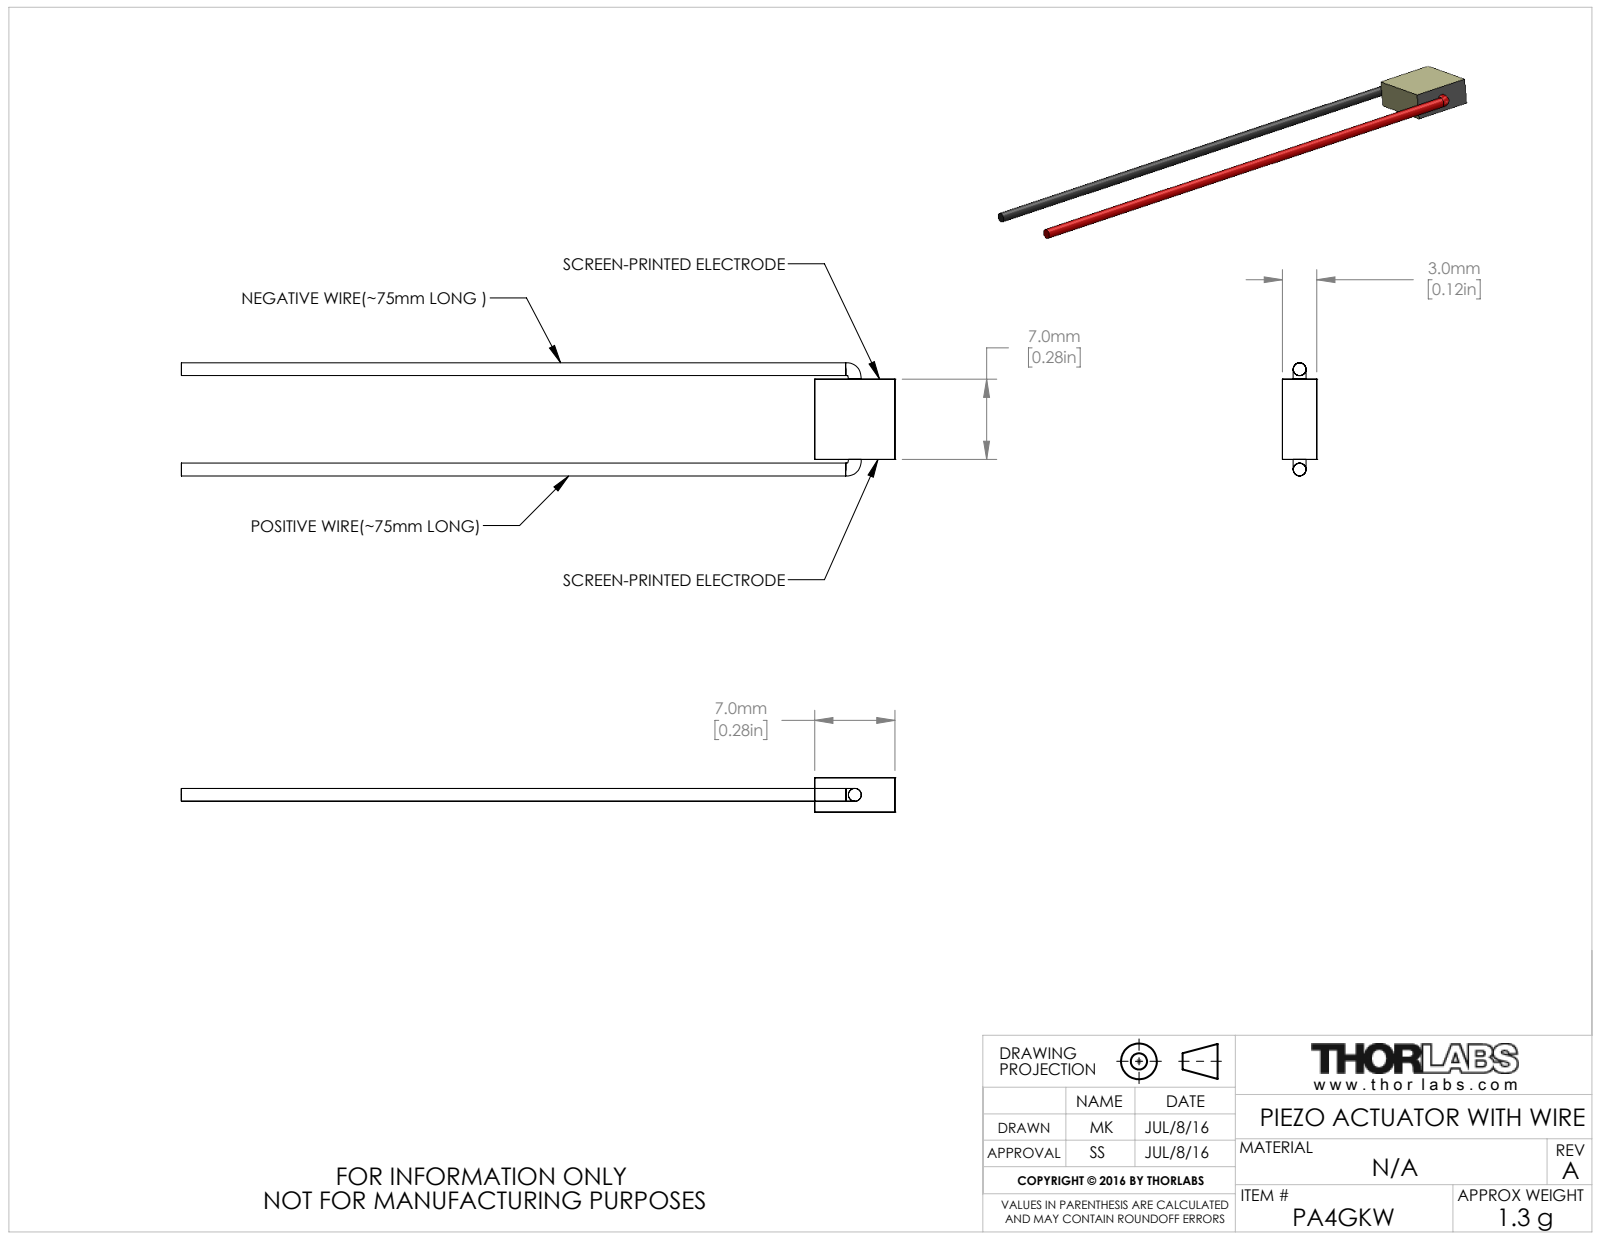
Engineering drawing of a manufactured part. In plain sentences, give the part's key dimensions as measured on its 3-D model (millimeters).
The part is named "CTN003169". Its 3-D file was written by "SolidWorks 2016 (AUTOMOTIVE_DESIGN)". It is 3 solids with 18 faces: 10 planar, 0 cylindrical and 8 other. Overall it measures 62.29 by 9.88 by 3 millimeters. Its volume is 264 cubic millimeters and its surface area 604 square millimeters. The main face-to-face distances are 3, 7, 62.29, 55.29.
